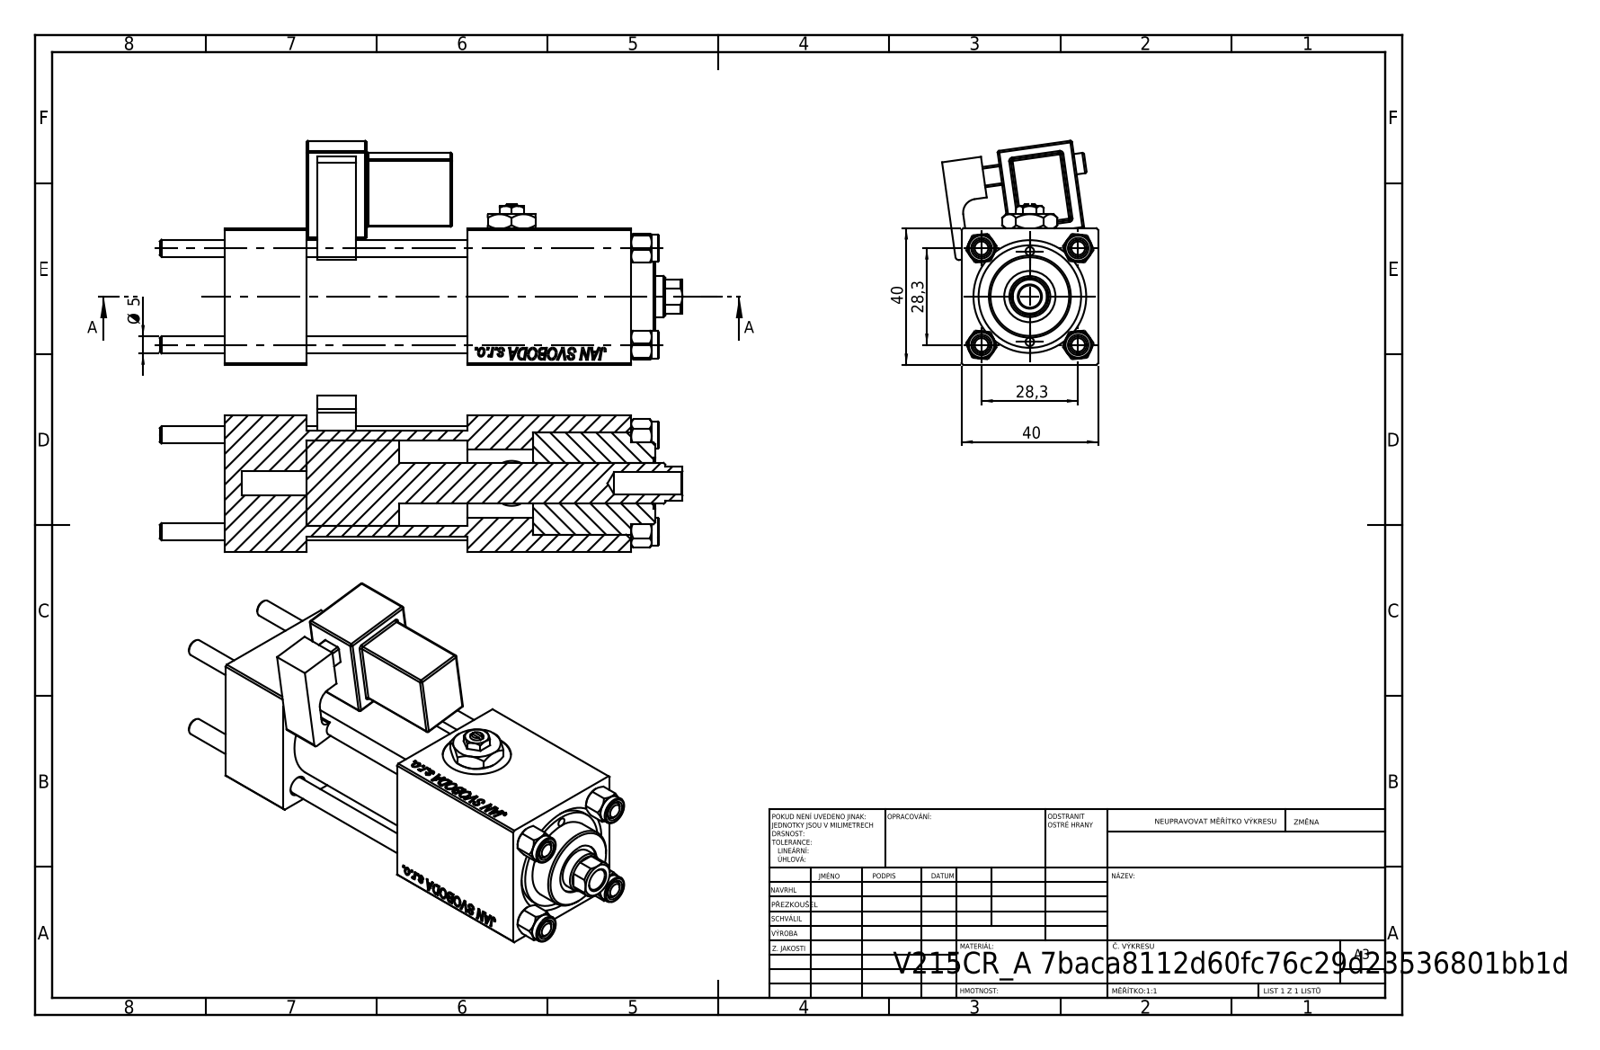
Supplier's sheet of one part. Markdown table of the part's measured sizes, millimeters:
| quantity | value |
| --- | --- |
| part name | NUT_M5; V215CR_VCP; V215_VC_A; Zatka_pro_OIL_PORT (+3 more) |
| STEP written by | SolidWorks 2019 (CONFIG_CONTROL_DESIGN) |
| units | millimeters |
| bodies | 13 solids, 1264 faces (574 planar, 116 cylindrical, 574 other) |
| overall size | 153 × 65.59 × 45.69 |
| volume | 164 407 mm³ |
| surface area | 65 673 mm² |
| round holes (diameter × count) | 5 × 4, 20 × 3, 2.5 × 2, 7 × 2, 13.16 × 2, 6.5 × 1, 12 × 1, 15 × 1, 25 × 1, 30 × 1 |
| round bosses / shafts (diameter × count) | 8 × 4, 31 × 1, 24 × 1, 6 × 1 |
| partial cylindrical surfaces (radius × count) | 0.5 × 24, 1 × 1, 2.5 × 1, 4 × 1, 5.5 × 1 |
| main face-to-face distances | 40, 24, 3, 119, 95, 90.3, 66.3, 28.7, 47, 71 |
| hole center spacings | 14.18, 20.01, 28.3, 30.84, 13.25, 40.02, 26.5, 72 |
